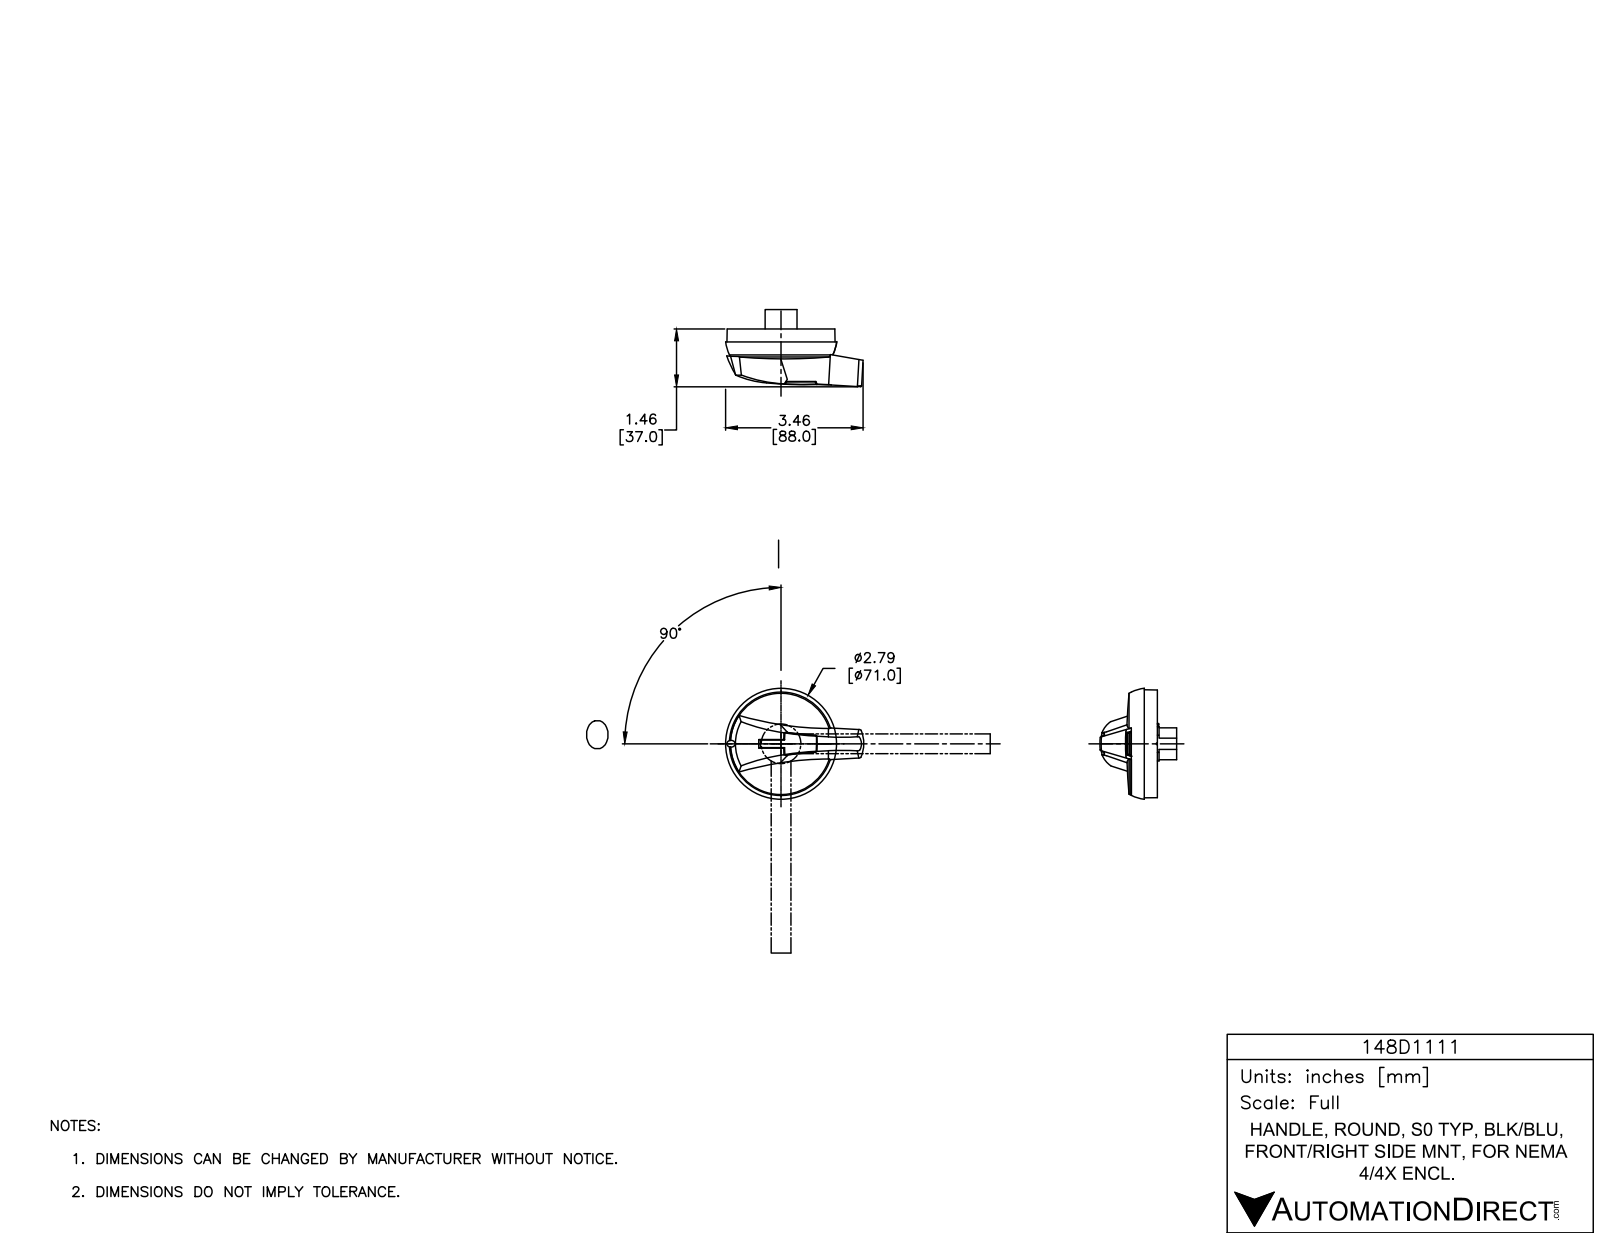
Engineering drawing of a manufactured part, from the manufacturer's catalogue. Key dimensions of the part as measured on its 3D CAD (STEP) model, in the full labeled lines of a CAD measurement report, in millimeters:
Part name (STEP PRODUCT): 148D1111
STEP written by: SolidWorks 2015 (AUTOMOTIVE_DESIGN)
Units: millimetres
Bodies: 5 solids, 1981 faces (411 planar, 317 cylindrical, 1253 other)
Overall size (bounding box): 88.4 × 71.1 × 48.9
Volume: 53 420 mm³ · Surface area: 57 490 mm²
Round holes (diameter × count): ⌀4.3 ×4, ⌀4.9 ×4, ⌀10 ×4, ⌀2 ×3, ⌀3.3 ×2, ⌀4 ×2, ⌀8.5 ×2, ⌀3 ×1, ⌀3.2 ×1, ⌀11.6 ×1, ⌀66.5 ×1
Round bosses / shafts (diameter × count): ⌀65 ×1
Partial cylindrical surfaces — rounded edges, fillets, slot ends (radius × count): R0.5 ×96, R0.3 ×19, R1 ×11, R0.3 ×10, R0.8 ×8, R3.6 ×4, R4.7 ×4, R0.4 ×1
Main face-to-face distances: 1.5, 1.8, 3.3, 15.6, 1.3, 0.8, 14.1, 12.3, 3.9, 7.5
Hole centre spacings: 14.3, 24.4, 39.5, 30, 17, 17.2, 21.4, 28
